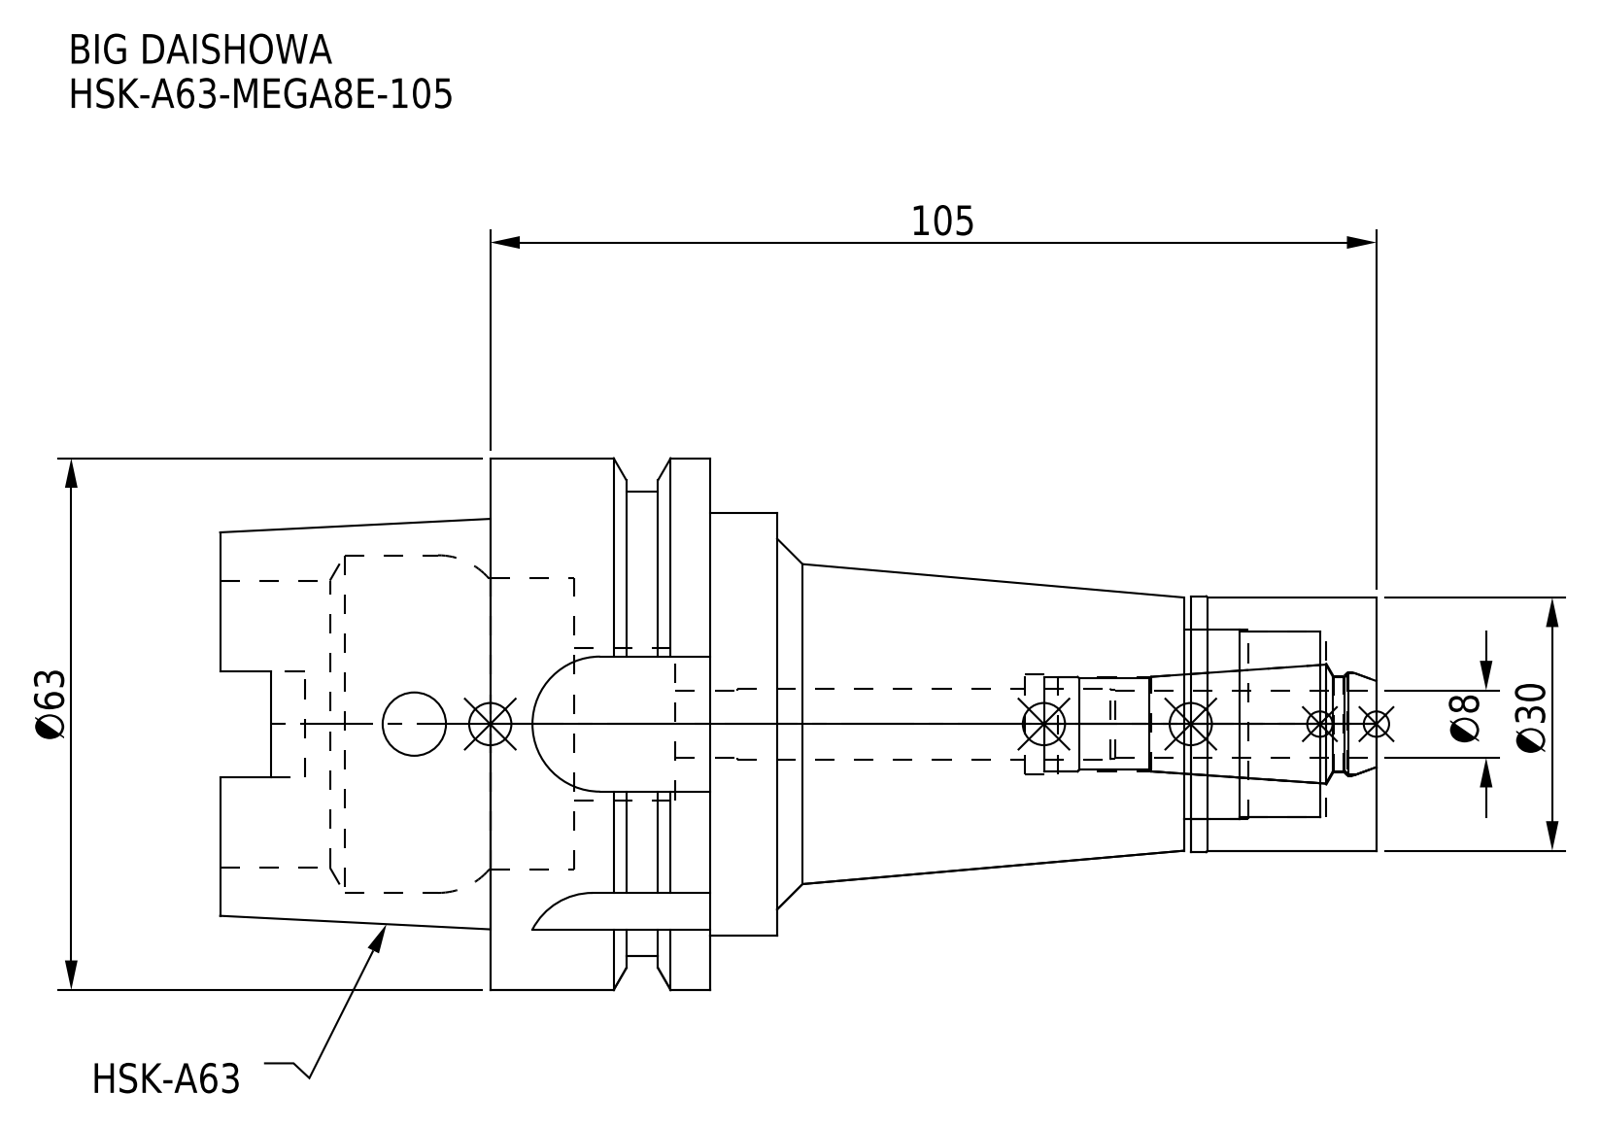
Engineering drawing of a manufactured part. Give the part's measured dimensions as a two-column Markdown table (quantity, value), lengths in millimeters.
| quantity | value |
| --- | --- |
| part name | HSK-A63-MEGA8E-105_1.stp; HSK-A63-MEGA8E-105-080-FreeParts; HSK-A63-MEGA8E-105-080.stp; DXF_TEMP_ASSY_ASM_4_ASM.stp (+3 more) |
| STEP written by | SolidWorks 2019 (CONFIG_CONTROL_DESIGN) |
| units | millimeters |
| bodies | 2 solids, 127 faces (45 planar, 54 cylindrical, 28 other) |
| overall size | 137 × 63 × 63 |
| volume | 151 341 mm³ |
| surface area | 36 203 mm² |
| round holes (diameter × count) | 7.5 × 1, 8 × 1, 8.4 × 1, 11.2 × 1, 11.4 × 1, 11.8 × 1, 12.3 × 1, 18 × 1, 22 × 1, 22.5 × 1, 34 × 1, 34.5 × 1 |
| round bosses / shafts (diameter × count) | 63 × 1, 55 × 1, 50 × 1, 30.3 × 1, 30 × 1 |
| partial cylindrical surfaces (radius × count) | 2.8 × 2, 2.88 × 2, 8 × 2, 9 × 1 |
| main face-to-face distances | 26, 105, 16.05, 9.95, 79, 95.05, 71, 8, 24.05, 34 |
